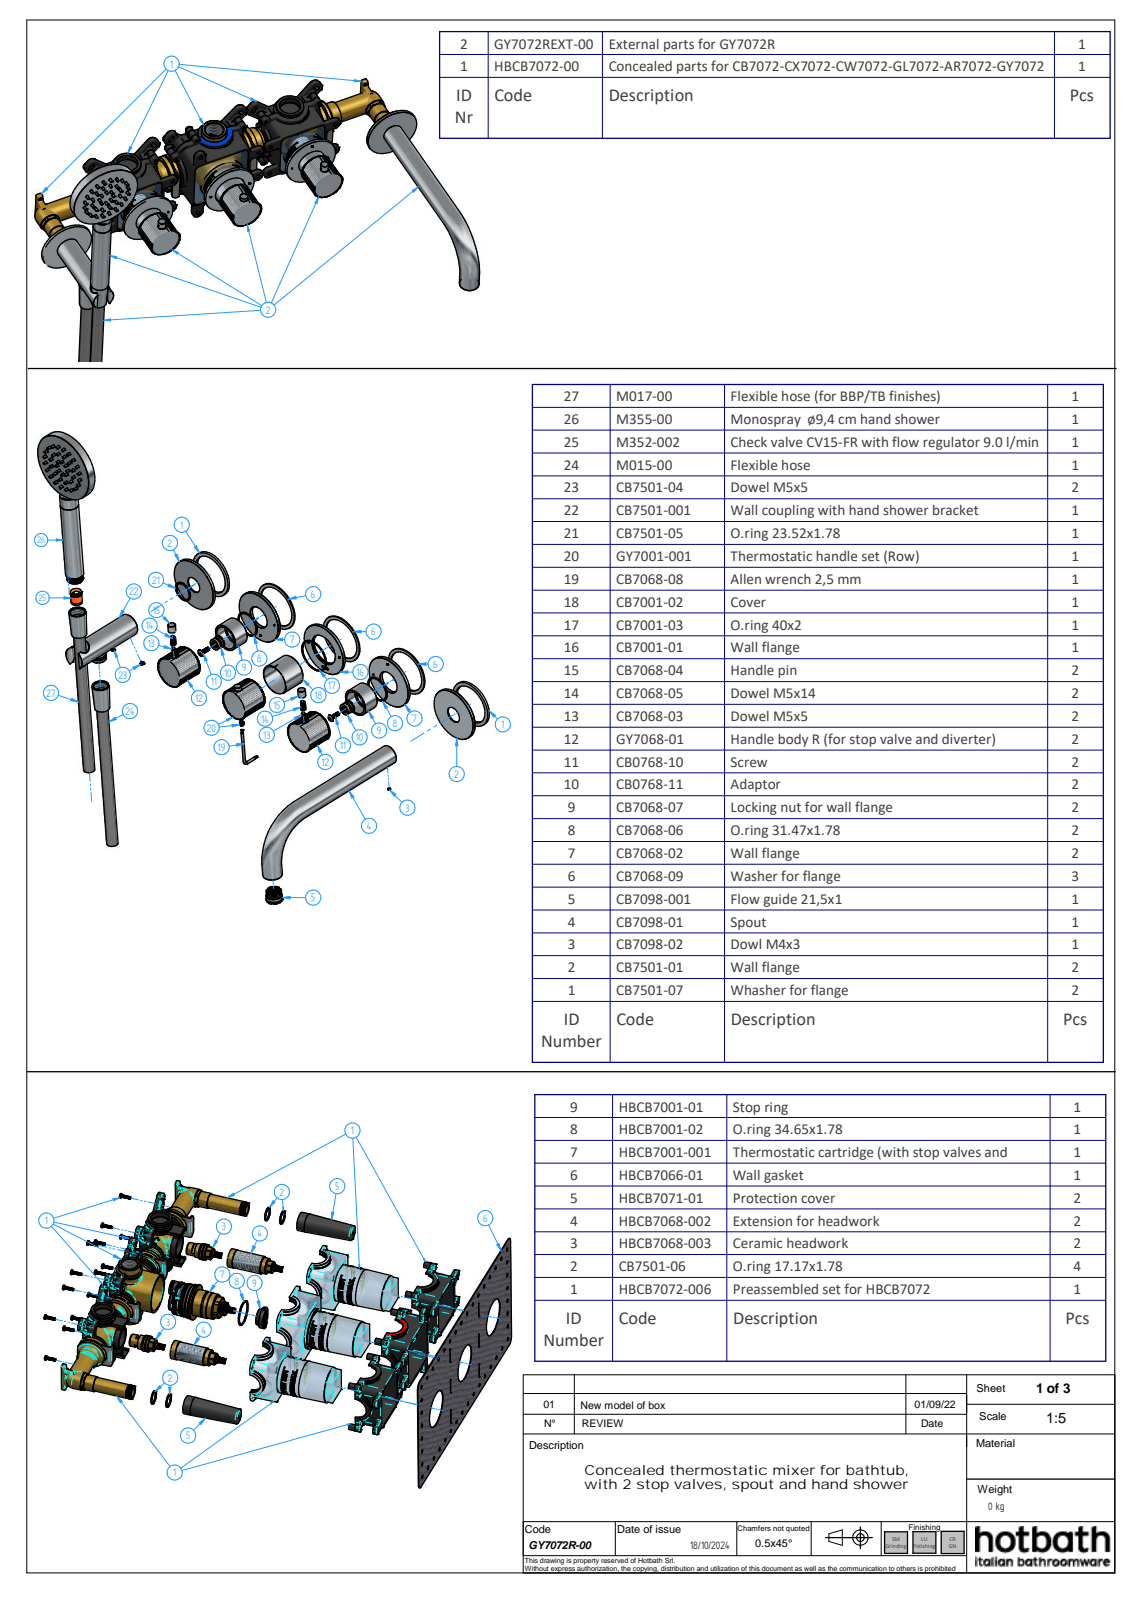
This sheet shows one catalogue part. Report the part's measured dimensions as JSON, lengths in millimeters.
{"part_name": "GY7072REXT-00; CB7098-01; CB7098-02; CB7098-001 (+8 more)", "step_written_by": "Solid Edge (AUTOMOTIVE_DESIGN)", "units": "millimeters", "bodies": {"solids": 53, "faces": 4262, "planar": 1280, "cylindrical": 1258, "other": 1724}, "overall_size": [563, 501.74, 258.2], "volume_mm3": 478493, "surface_area_mm2": 268142, "round_holes": [[0.7, 40], [4.13, 5], [5.2, 3], [15.2, 3], [38, 3], [57, 3], [67, 3], [4, 2], [4.5, 2], [10.5, 2], [16.5, 2], [18.63, 2]], "round_bosses_or_shafts": [[72, 5], [5, 5], [66, 3], [10, 3], [4, 3], [64, 2], [52, 2], [26, 2]], "partial_cylinders_radius": [[0.1, 531], [4.5, 12], [0.2, 8], [0.81, 6], [9.5, 4], [0.56, 2], [0.73, 2], [1, 2]], "face_to_face_distances": [1.5, 3, 2, 4, 10, 12, 89.8, 85.8, 1.9, 101.8], "hole_center_spacings": [37.62, 63.22, 10.01, 19.78, 51.78, 57.03, 29.06, 45.26]}
